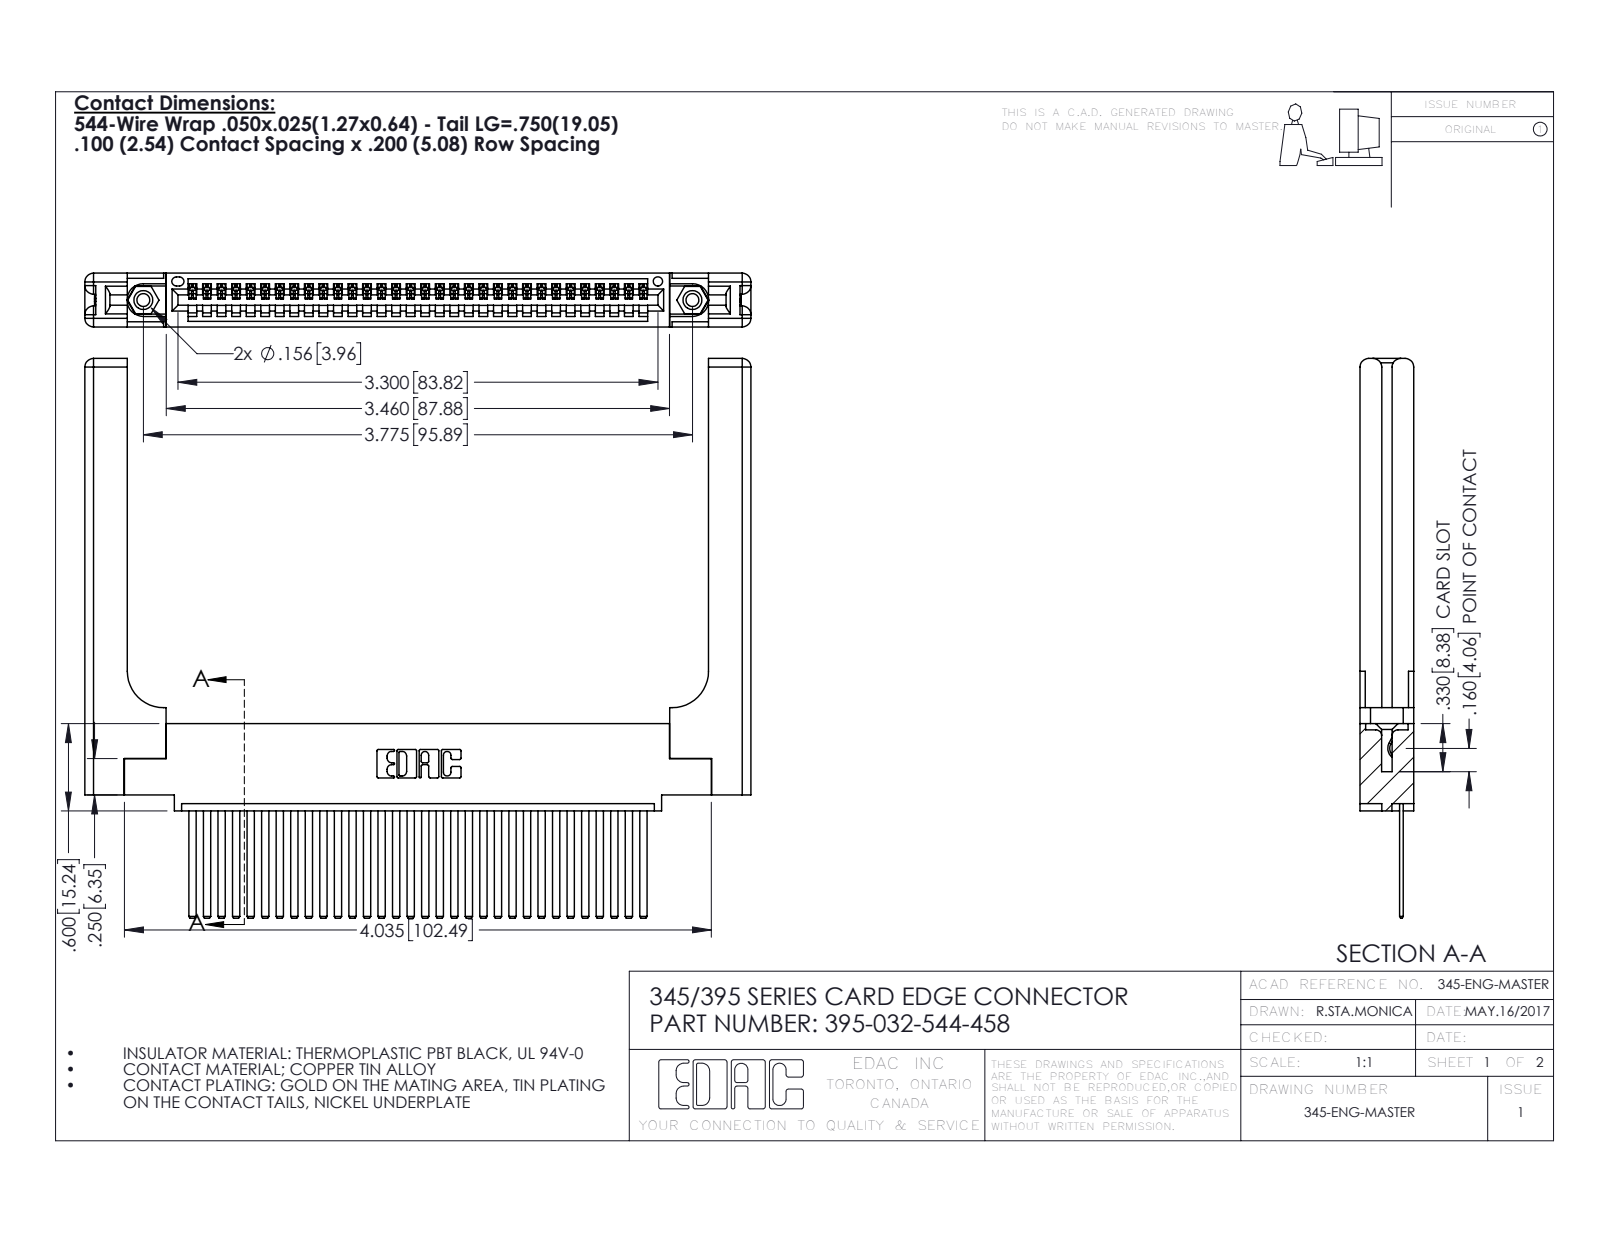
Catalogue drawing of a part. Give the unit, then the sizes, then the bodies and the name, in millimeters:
Units: millimetres
Overall size (bounding box): 116.3 × 97.7 × 9.4
Round holes (diameter × count): ⌀2.3 ×2, ⌀3.2 ×2, ⌀4 ×2, ⌀1.6 ×1
Round bosses / shafts (diameter × count): ⌀3.9 ×2
Partial cylindrical surfaces — rounded edges, fillets, slot ends (radius × count): R0.2 ×64, R0.3 ×22, R1.5 ×16, R0.2 ×6, R0.8 ×6, R0.7 ×3, R0.8 ×2, R0.8 ×2
Main face-to-face distances: 1.8, 7.6, 9.4, 2.5, 6.9, 0.6, 5.1, 3.8, 3.8, 2
Hole centre spacings: 6.9, 89.9, 95.9
Volume: 19 760 mm³ · Surface area: 21 330 mm²
Bodies: 37 solids, 2050 faces (1384 planar, 606 cylindrical, 60 other)
Part name (STEP PRODUCT): 395-032-544-458; 345-250-001_345-250-001-102; 345 Part_0.110 Offset - 0.156 Dia-TH; 345-292-001_345-293-144 (+1 more)
STEP written by: SolidWorks 2016 (CONFIG_CONTROL_DESIGN)
